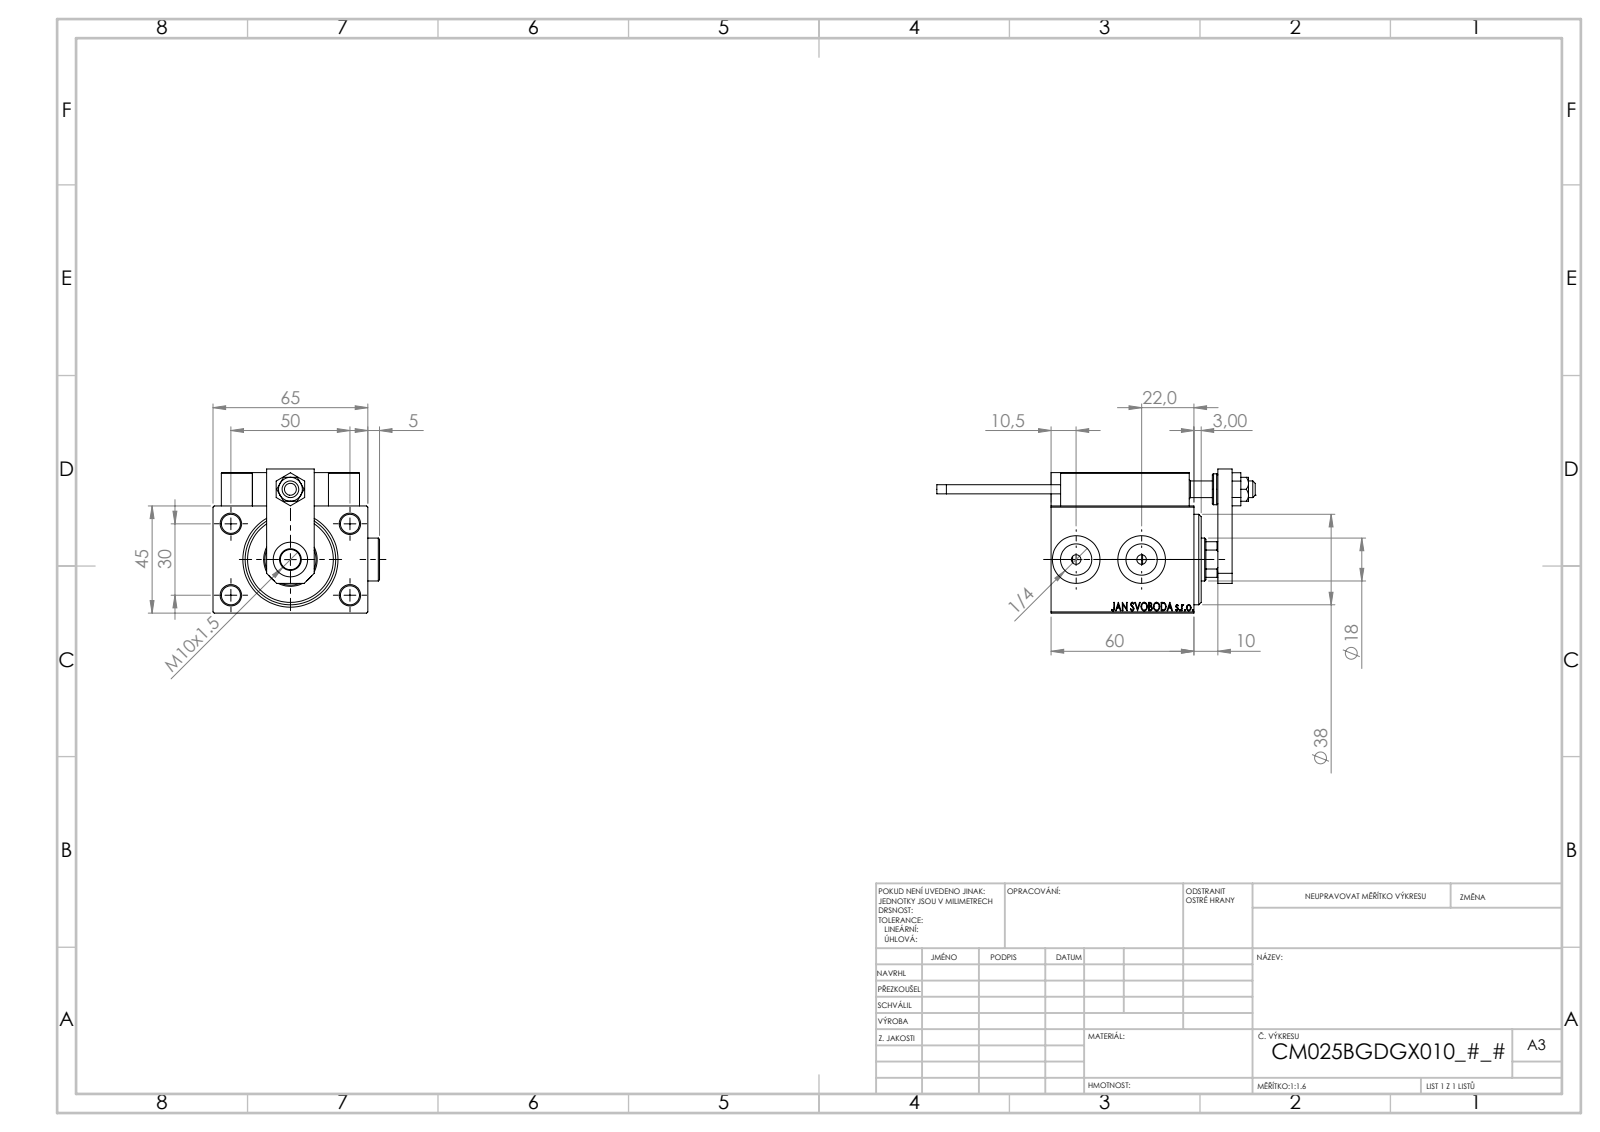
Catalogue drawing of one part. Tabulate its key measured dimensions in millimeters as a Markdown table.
| quantity | value |
| --- | --- |
| part name | ALLEN BOLT D8; SWITCH X; NUT_D10; ZARAZKA (+7 more) |
| STEP written by | SolidWorks 2019 (CONFIG_CONTROL_DESIGN) |
| units | millimeters |
| bodies | 26 solids, 1372 faces (597 planar, 198 cylindrical, 577 other) |
| overall size | 133.7 × 69.9 × 60.5 |
| volume | 209 847 mm³ |
| surface area | 64 223 mm² |
| round holes (diameter × count) | 8 × 9, 4 × 6, 3.2 × 4, 5 × 2, 13.16 × 2, 20 × 2, 7 × 1, 8.5 × 1, 14.5 × 1, 18 × 1, 21.5 × 1, 22.5 × 1 |
| round bosses / shafts (diameter × count) | 18 × 2, 5 × 2, 3.8 × 2, 13 × 1, 11 × 1 |
| partial cylindrical surfaces (radius × count) | 0.3 × 30, 3 × 2, 8.5 × 1 |
| main face-to-face distances | 45, 10, 14, 59, 5, 7, 65, 13, 6, 60 |
| hole center spacings | 29.15, 11.37, 12.17, 20, 25.06, 28.9, 29.59, 29.69 |
